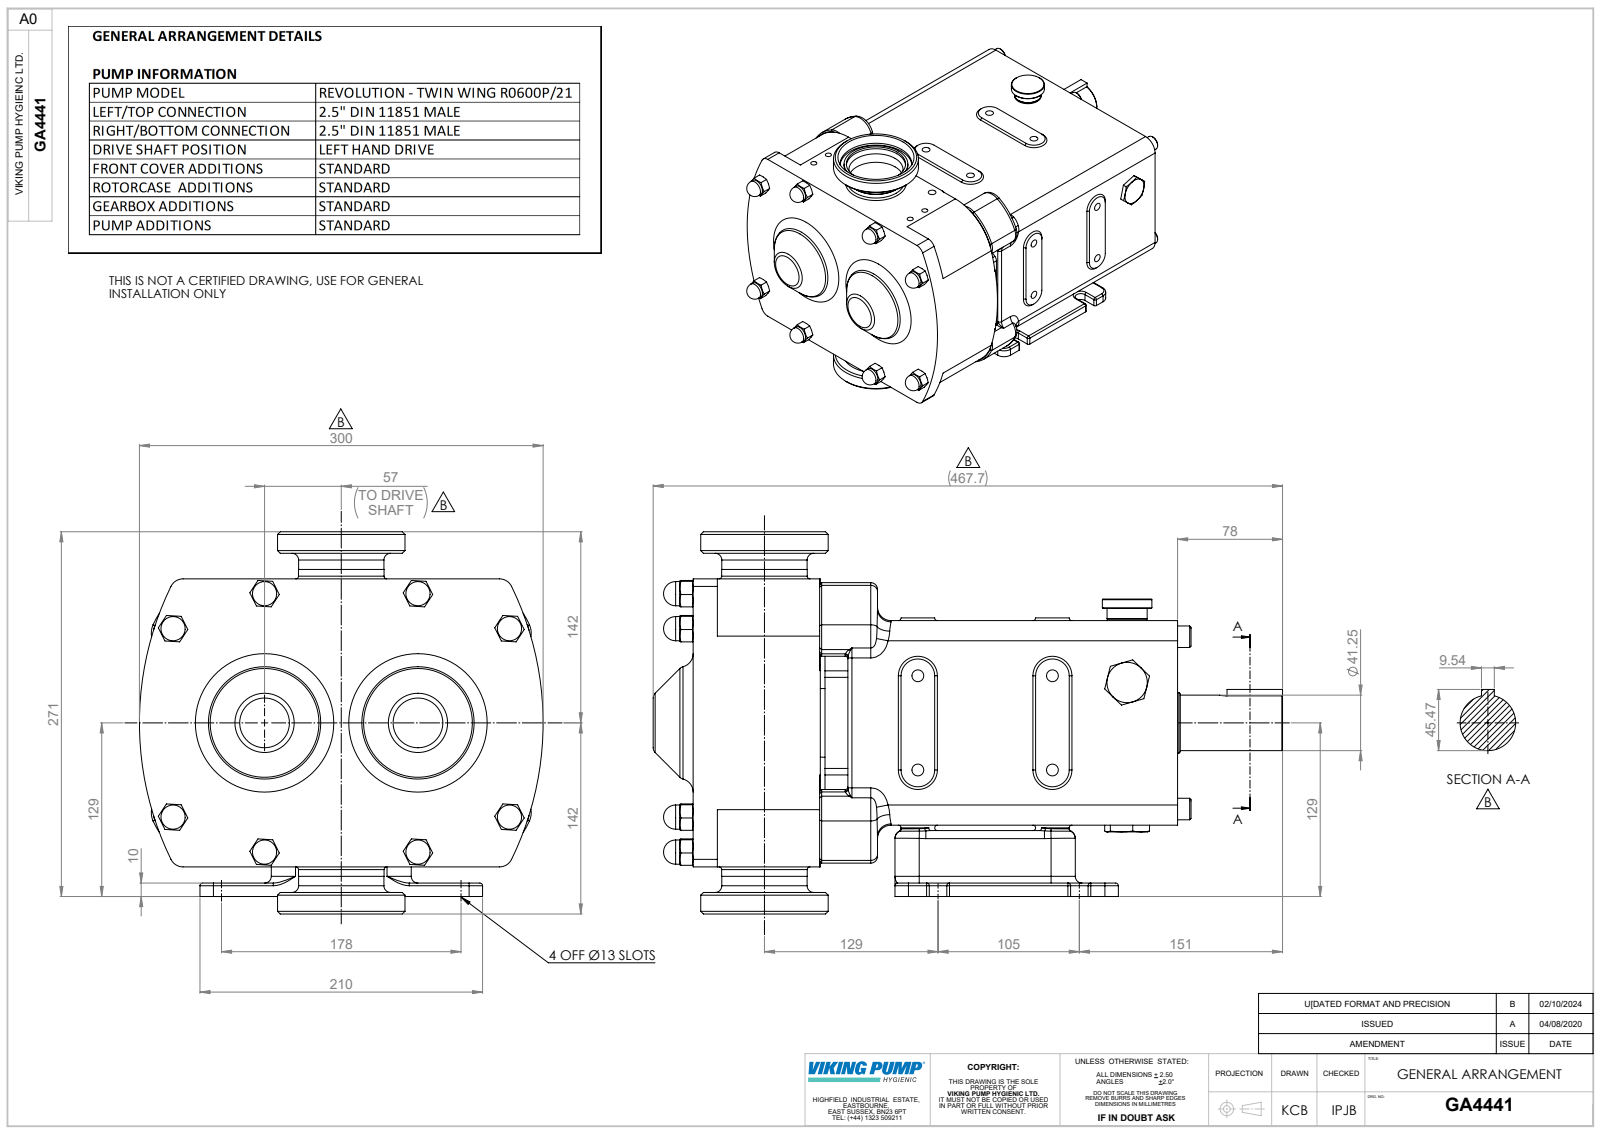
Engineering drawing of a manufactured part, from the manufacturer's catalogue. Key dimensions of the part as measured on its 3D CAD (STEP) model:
Part name (STEP PRODUCT): Copy of Z94-5031-44 - 2.5 INCH DIN11851^GA4441; Copy of R0600 CPP V LHD^GA4441; GA4441
STEP written by: SolidWorks 2023 (AUTOMOTIVE_DESIGN)
Units: millimetres
Bodies: 3 solids, 941 faces (292 planar, 287 cylindrical, 362 other)
Overall size (bounding box): 467.7 × 300 × 284
Volume: 17 300 000 mm³ · Surface area: 699 630 mm²
Round holes (diameter × count): ⌀8.8 ×8, ⌀6.8 ×4, ⌀8.6 ×2, ⌀33.8 ×1, ⌀60.3 ×1, ⌀66 ×1, ⌀80 ×1
Round bosses / shafts (diameter × count): ⌀18 ×8, ⌀16 ×6, ⌀94.7 ×1, ⌀71.1 ×1, ⌀63.6 ×1, ⌀63.4 ×1, ⌀51 ×1, ⌀45 ×1
Partial cylindrical surfaces — rounded edges, fillets, slot ends (radius × count): R2 ×38, R10 ×30, R5 ×19, R5.9 ×8, R15 ×8, R18 ×8, R3 ×4, R6 ×4
Main face-to-face distances: 152, 94.5, 265.5, 360, 3.5, 262, 98, 43, 266, 31
Hole centre spacings: 70, 100, 122.07, 239.53, 23, 35.93, 56.77, 65.12
